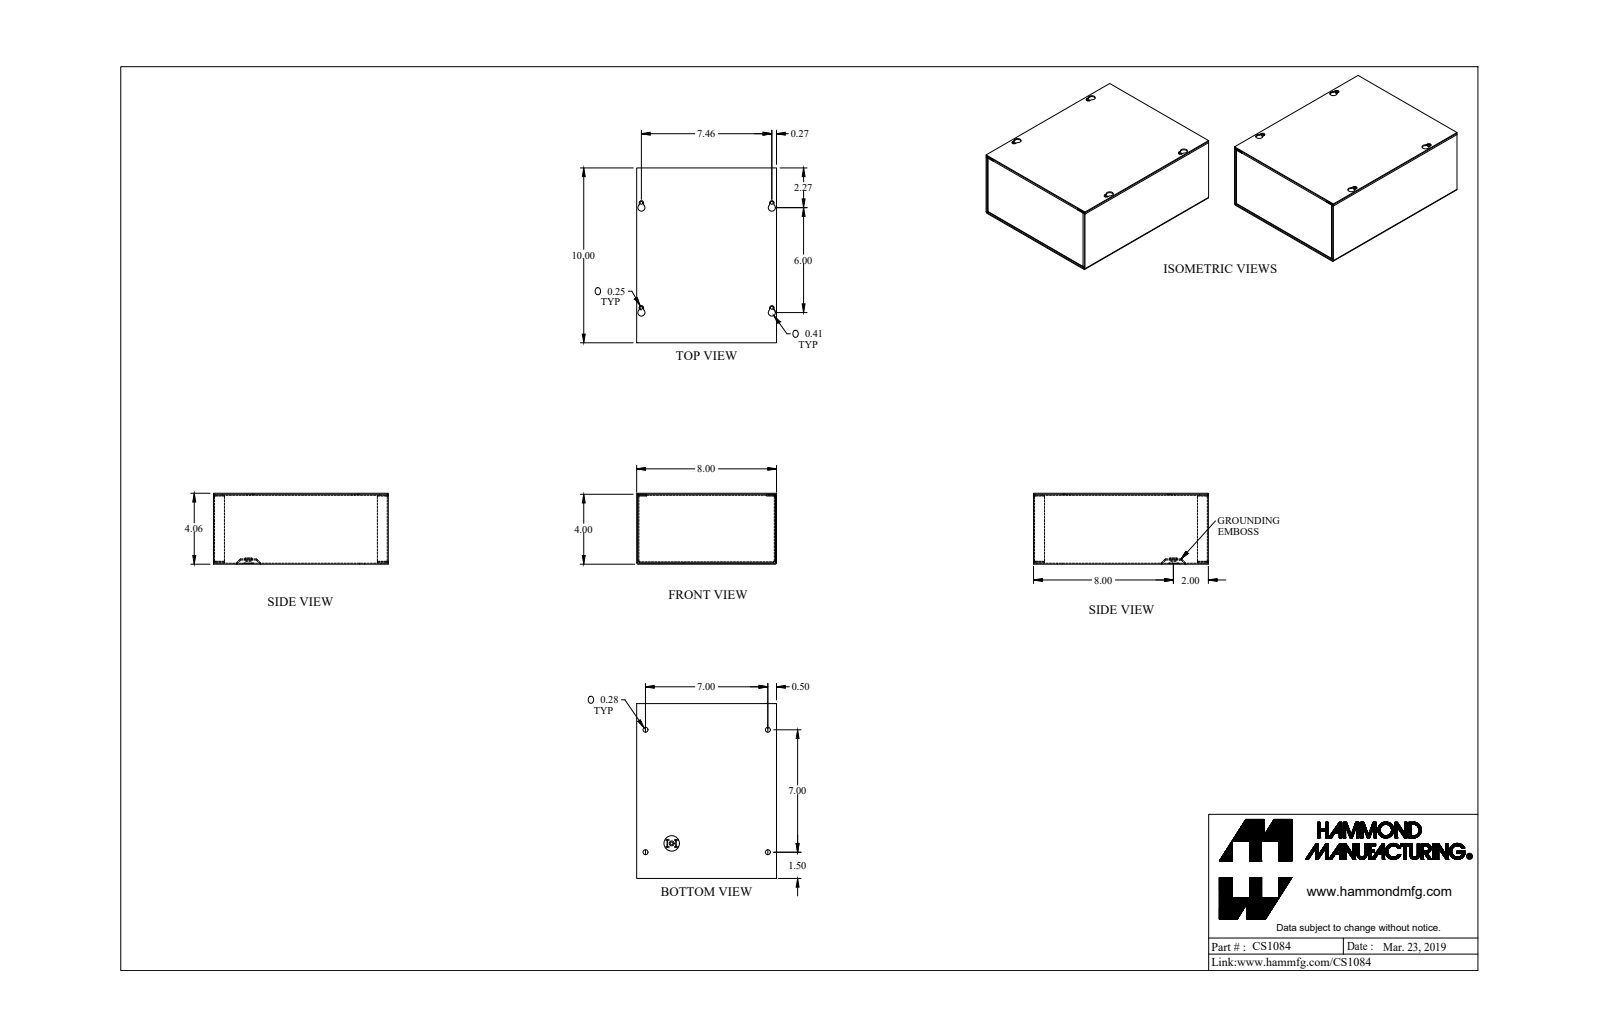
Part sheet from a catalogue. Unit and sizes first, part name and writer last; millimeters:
Units: millimetres
Overall size (bounding box): 254 × 203.2 × 103
Round holes (diameter × count): ⌀4.3 ×5, ⌀7.1 ×4, ⌀12.7 ×1
Round bosses / shafts (diameter × count): ⌀12.5 ×1, ⌀7.2 ×1
Partial cylindrical surfaces — rounded edges, fillets, slot ends (radius × count): R0.7 ×12, R2.2 ×12, R1.4 ×8, R3.2 ×4, R5.2 ×4
Main face-to-face distances: 1.4, 101.6, 100.2, 201.8, 103, 252.6, 203.2, 200.3, 254, 251.1
Hole centre spacings: 14, 165.2, 177.8, 184.1, 246.9, 152.4, 189.5, 243.2
Volume: 307 900 mm³ · Surface area: 431 300 mm²
Bodies: 4 solids, 205 faces (125 planar, 72 cylindrical, 8 other)
Part name (STEP PRODUCT): CS1084_Default
STEP written by: SolidWorks 2019 (CONFIG_CONTROL_DESIGN)
